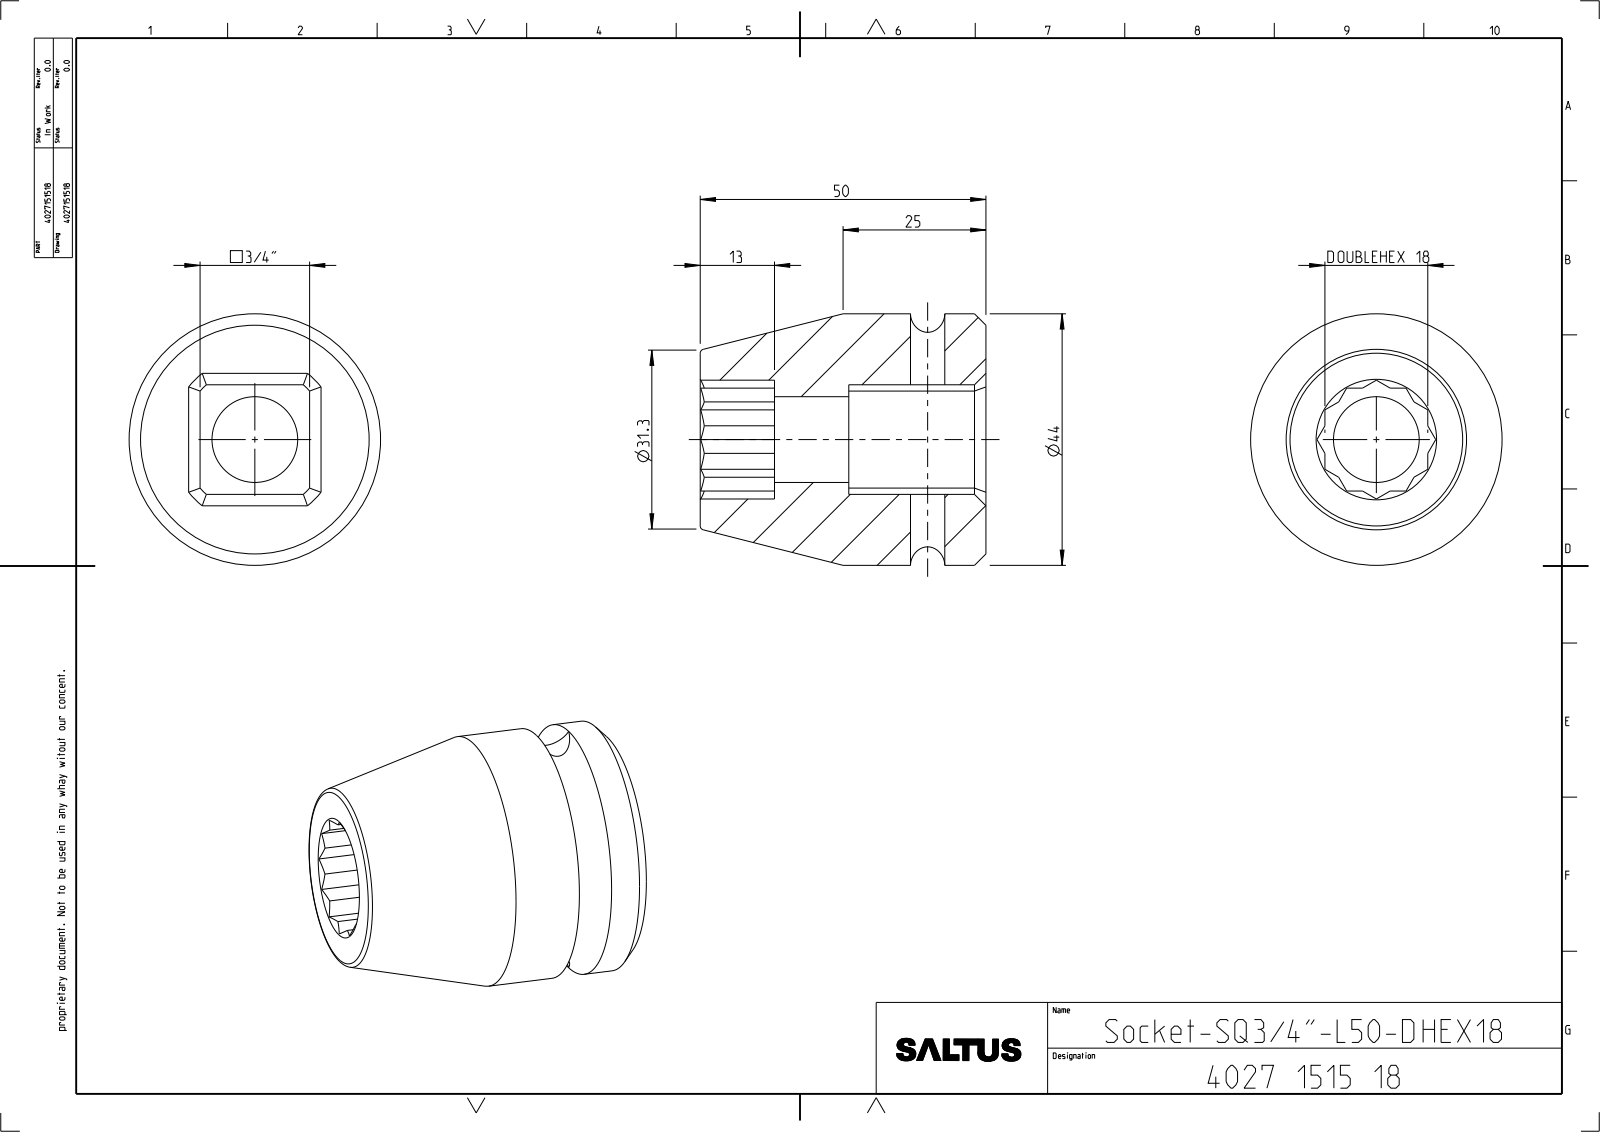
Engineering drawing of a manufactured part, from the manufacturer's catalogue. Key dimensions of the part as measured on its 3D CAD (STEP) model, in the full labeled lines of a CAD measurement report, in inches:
Part name (STEP PRODUCT): 4027151518
STEP written by: CREO PARAMETRIC BY PTC INC, 2022414 (CONFIG_CONTROL_DESIGN)
Units: inches
Bodies: 1 solid, 64 faces (36 planar, 14 cylindrical, 14 other)
Overall size (bounding box): 1.969 × 1.732 × 1.732
Volume: 2.948 in³ · Surface area: 18.66 in²
Round holes (diameter × count): ⌀0.236 ×1, ⌀0.591 ×1
Round bosses / shafts (diameter × count): ⌀1.732 ×1
Partial cylindrical surfaces — rounded edges, fillets, slot ends (radius × count): R0.504 ×1
Main face-to-face distances: 0.755, 0.709, 1.969, 0.023, 0.732, 0.512, 0.945, 1.024, 1.457
